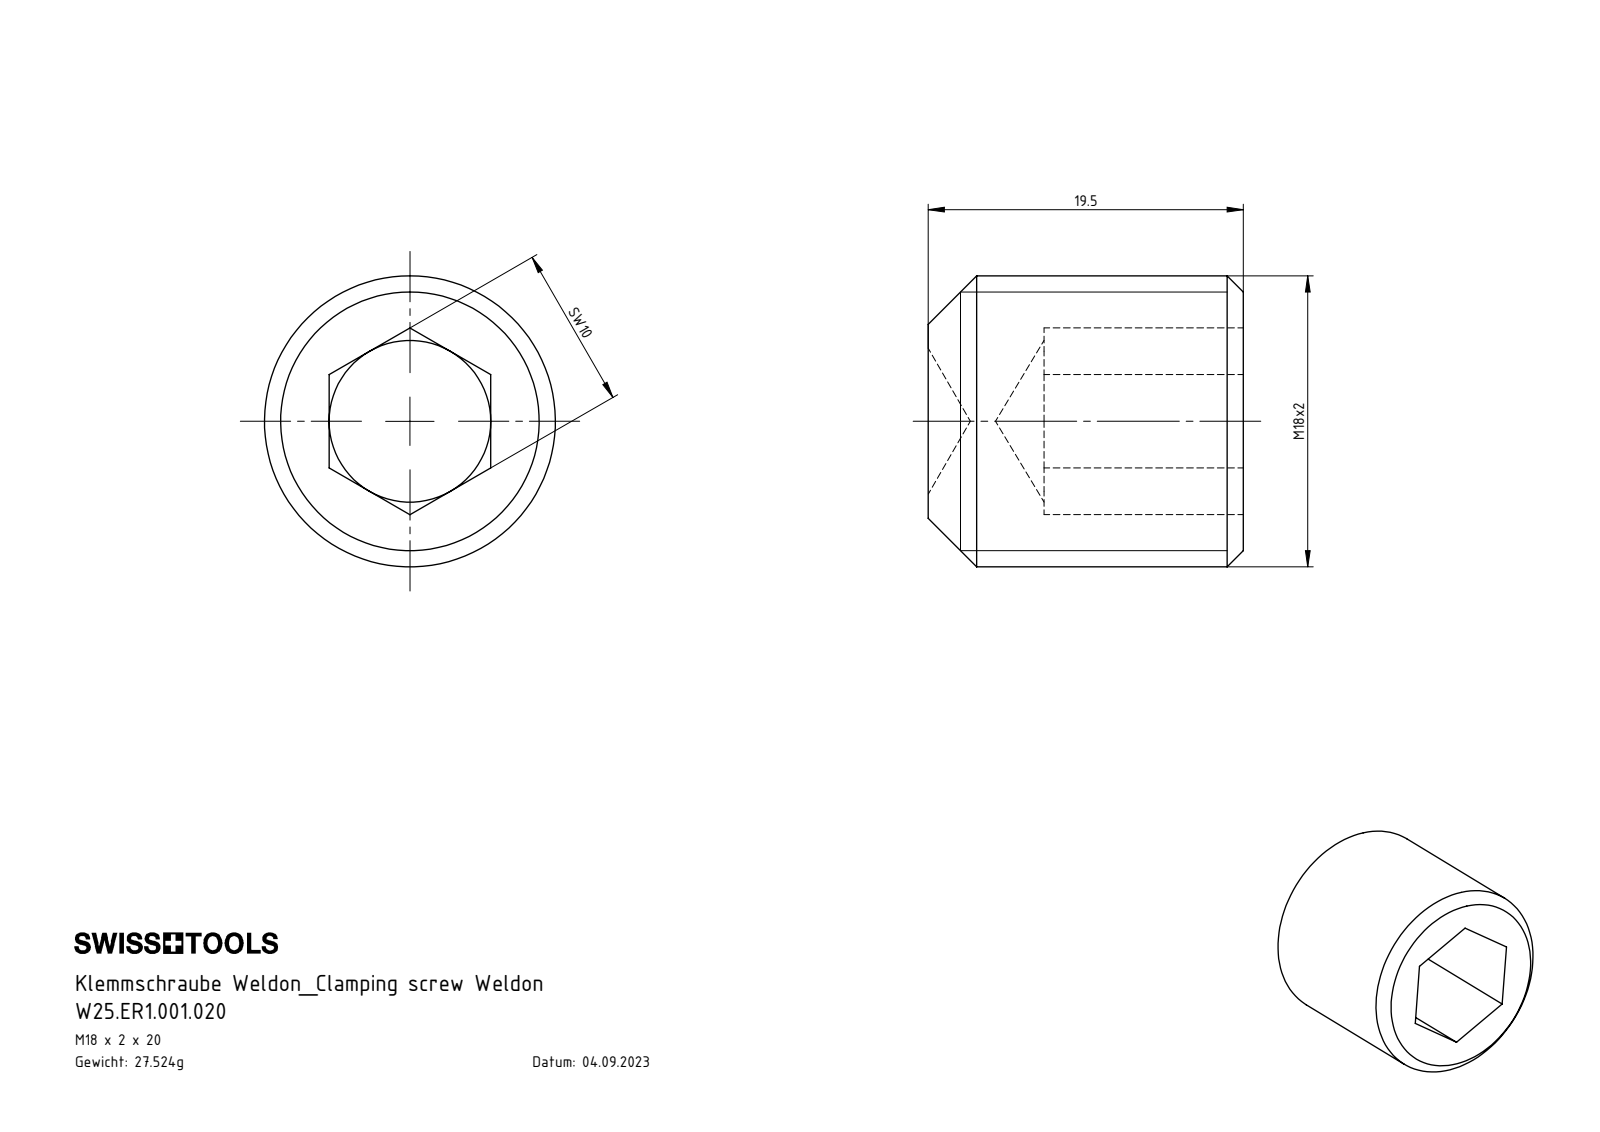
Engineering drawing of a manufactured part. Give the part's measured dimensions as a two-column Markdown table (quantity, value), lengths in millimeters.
| quantity | value |
| --- | --- |
| part name | W25.ER1.001.020 |
| STEP written by | SolidWorks 2017 (AUTOMOTIVE_DESIGN) |
| units | millimeters |
| bodies | 1 solid, 24 faces (14 planar, 2 cylindrical, 8 other) |
| overall size | 19.5 × 18 × 18 |
| volume | 3 506 mm³ |
| surface area | 1 917 mm² |
| round bosses / shafts (diameter × count) | 18 × 1 |
| main face-to-face distances | 10, 19.5, 12.34, 7.16 |
